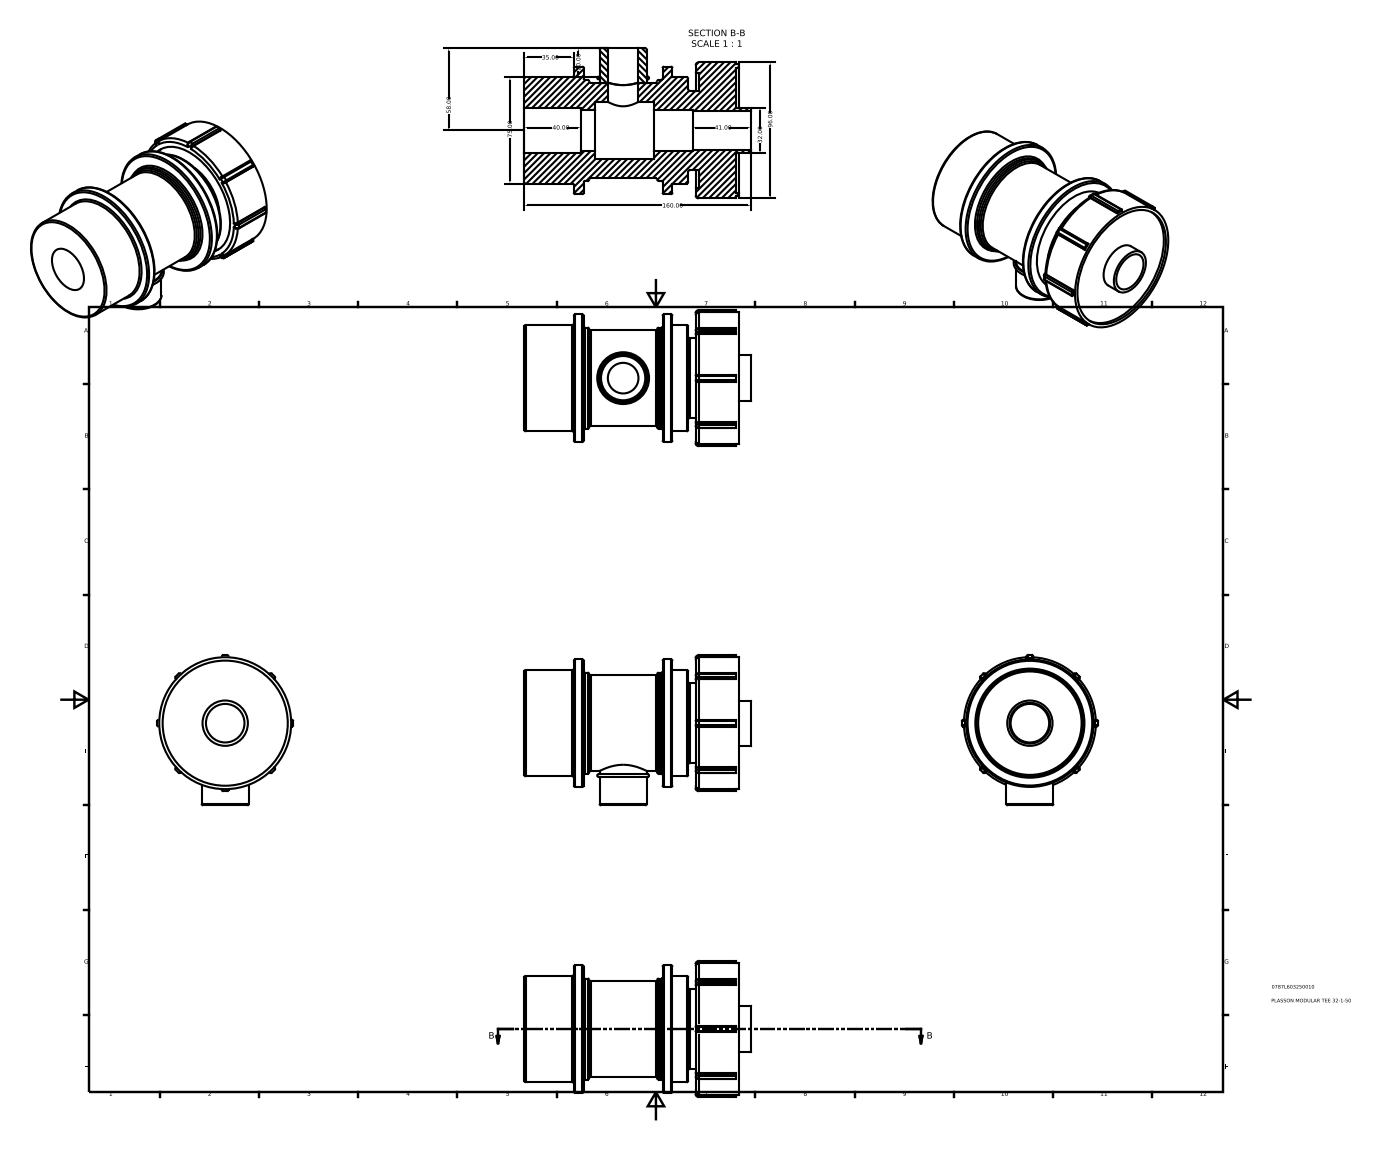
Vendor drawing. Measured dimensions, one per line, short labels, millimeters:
name: 0787L603250010
written by: Autodesk Inventor 2015 (AUTOMOTIVE_DESIGN)
unit: mm
bodies: 2 solids, 168 faces (50 planar, 62 cylindrical, 56 other)
size: 160 × 106 × 96
volume: 583 458 mm³; area: 87 180 mm²
holes: 1× ⌀21.61, 1× ⌀27.2, 1× ⌀28.8, 1× ⌀32, 1× ⌀40.32, 1× ⌀67.5, 1× ⌀81.6, 1× ⌀88.32
bosses: 1× ⌀93.12, 1× ⌀90, 1× ⌀75, 1× ⌀71.25, 1× ⌀56.25, 1× ⌀33.25
rounds: 28× R1, 8× R2
face distances: 149.75, 7.01, 62.65, 123.1, 26.65, 42.01, 81.09, 107.74, 97.65, 55.64
